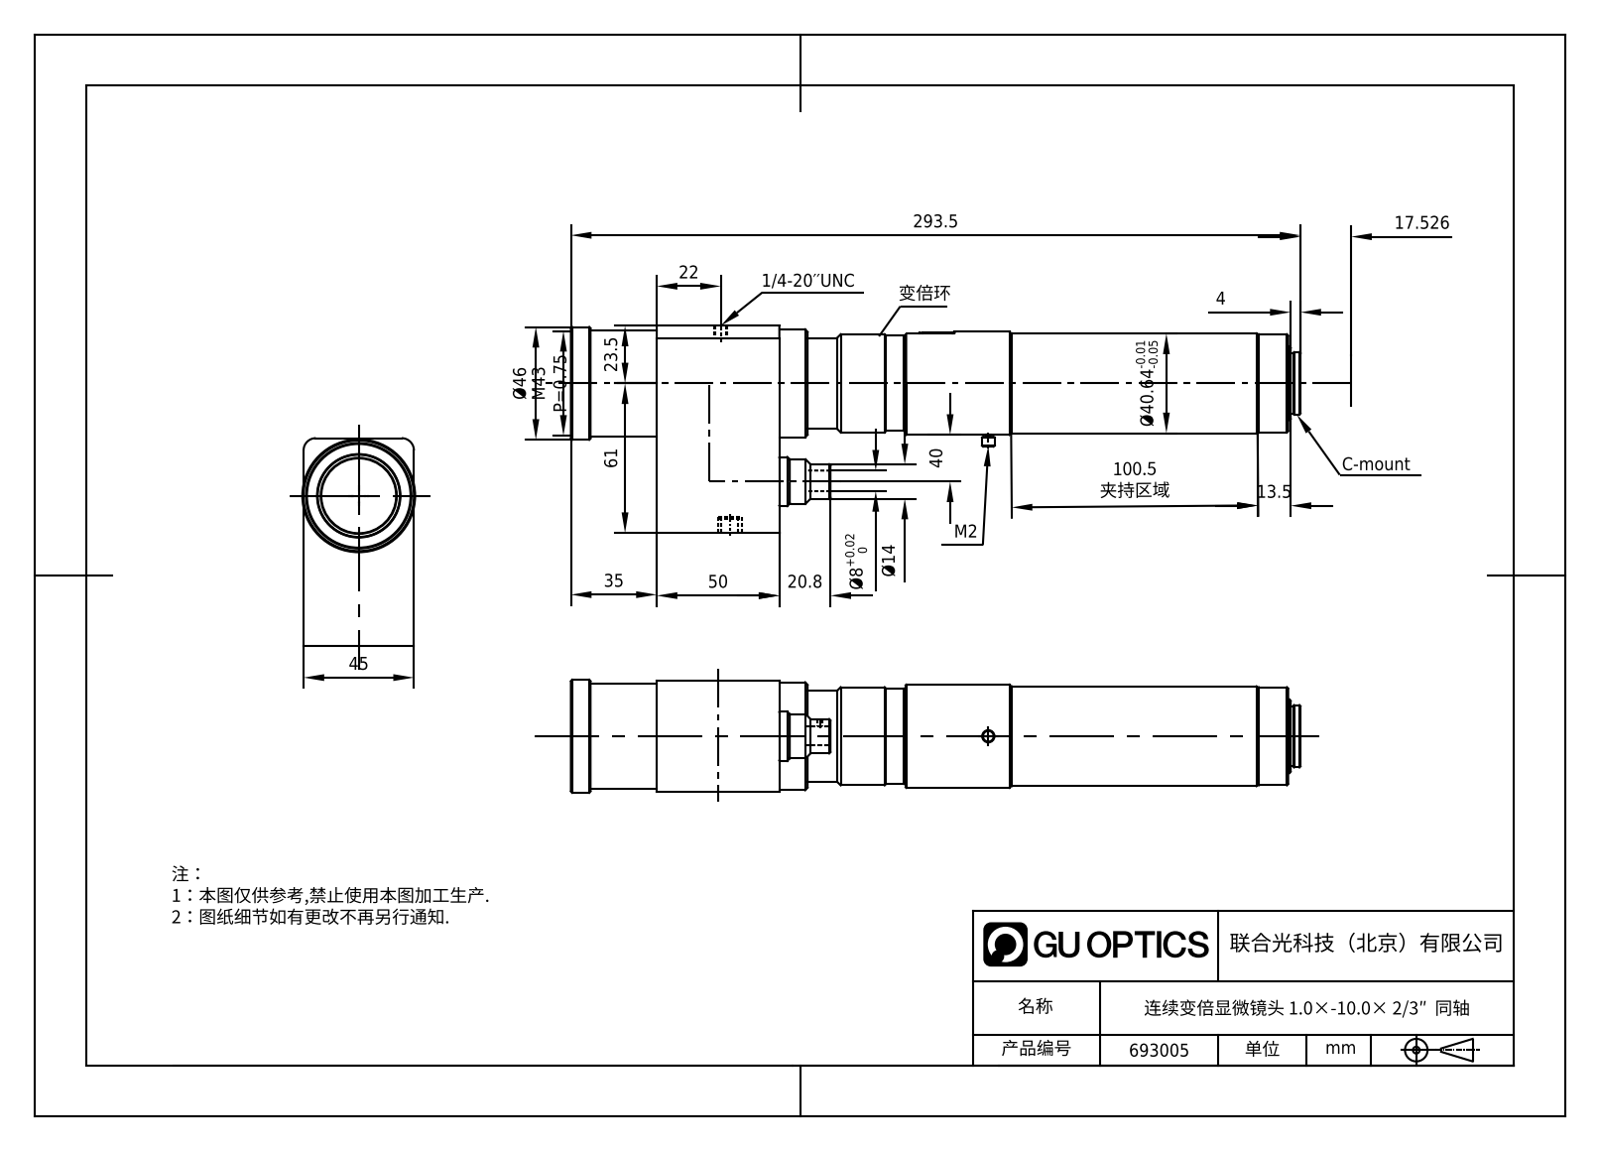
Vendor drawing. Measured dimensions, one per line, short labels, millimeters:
name: VSZ-10100COL
written by: SolidWorks 2016 (CONFIG_CONTROL_DESIGN)
unit: mm
bodies: 1 solid, 204 faces (45 planar, 74 cylindrical, 85 other)
size: 297.48 × 84.5 × 46
volume: 510 198 mm³; area: 57 954 mm²
holes: 2× ⌀1.8, 2× ⌀8, 1× ⌀2, 1× ⌀5.2, 1× ⌀11.5, 1× ⌀14, 1× ⌀21.5, 1× ⌀26, 1× ⌀30.5, 1× ⌀34, 1× ⌀42.25
bosses: 1× ⌀46, 1× ⌀44, 1× ⌀43, 1× ⌀42, 1× ⌀40.64, 1× ⌀40, 1× ⌀38.8, 1× ⌀37
rounds: 2× R0.5, 2× R1.25, 2× R5
face distances: 45, 50, 84.5, 1, 3.47, 32.5, 82.5, 289.98, 257.48, 207.48
hole spacings: 5.1, 9.7, 5, 5.5, 40
